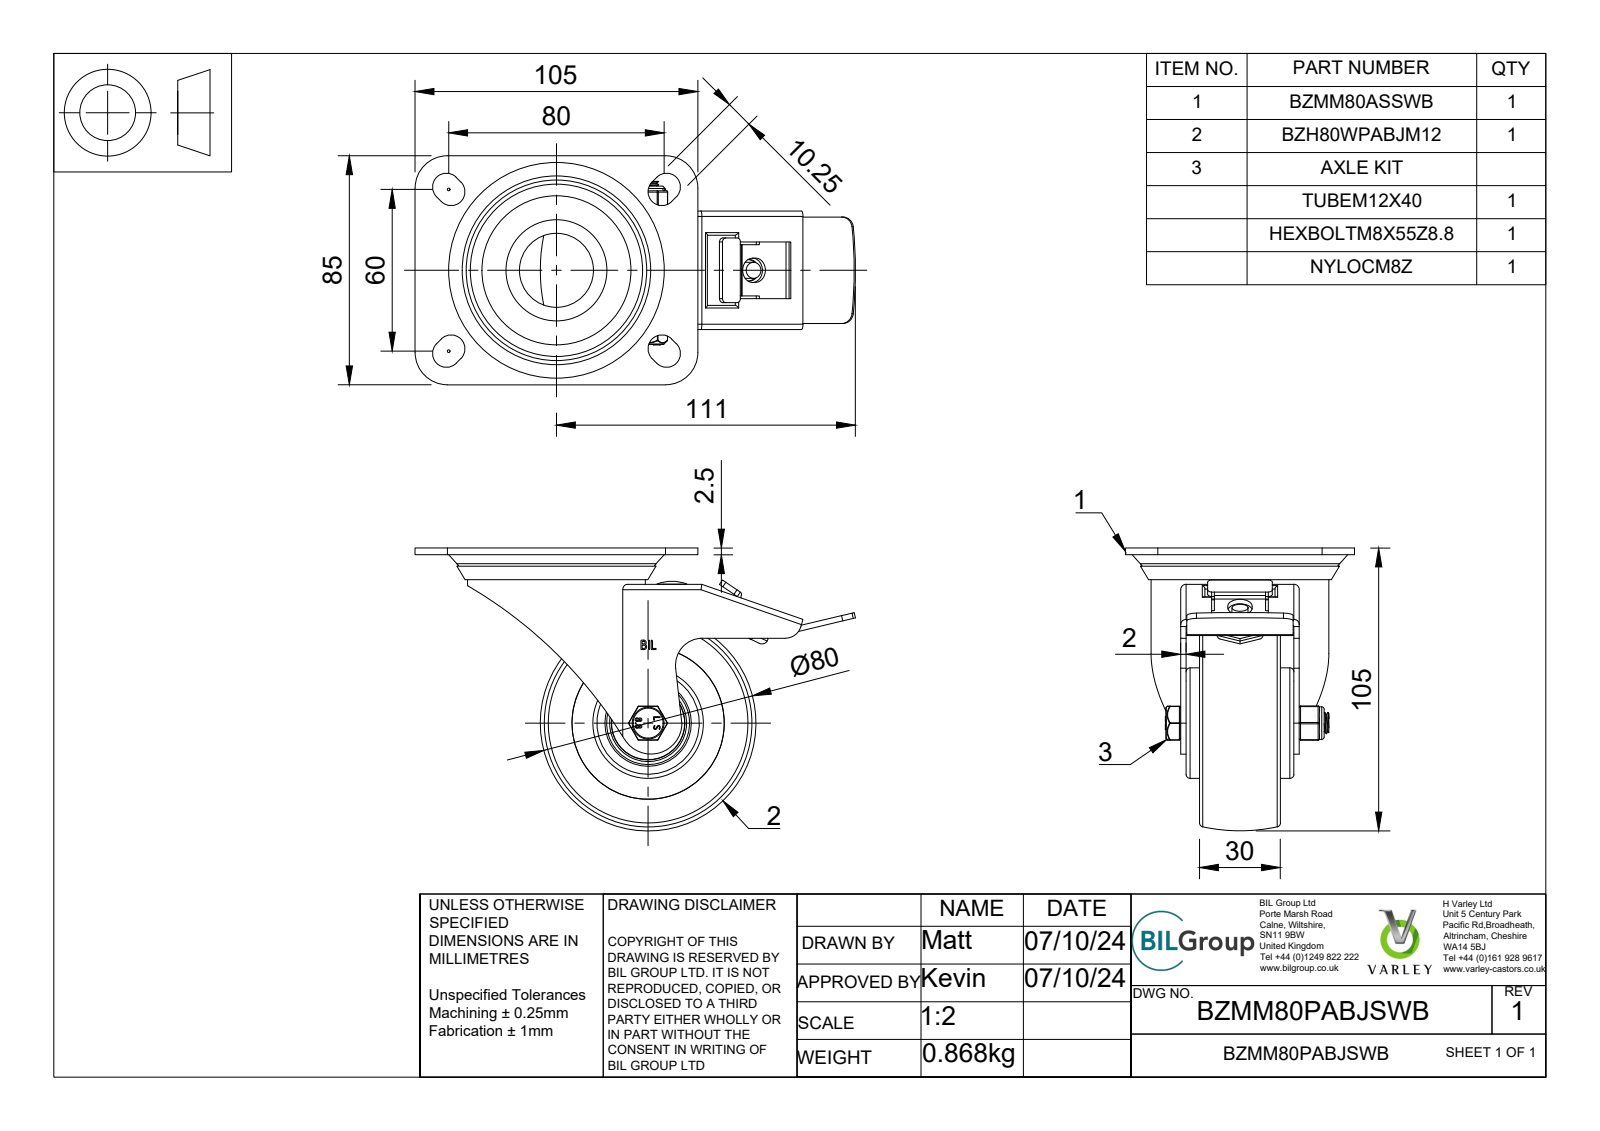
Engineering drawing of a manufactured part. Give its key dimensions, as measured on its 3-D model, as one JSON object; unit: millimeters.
{"part_name": "BZMM80PABJSWB v3; BZMM80ASSWB v1; ZINC PLATED, PRESSED STEEL TOP PLATE; ZINC PLATED, PRESSED STEEL TOP PLATE Geometry (+7 more)", "step_written_by": "Autodesk Translation Framework v13.20.0.188 (AUTOMOTIVE_DESIGN)", "units": "millimeters", "bodies": {"solids": 63, "faces": 1211, "planar": 503, "cylindrical": 230, "other": 478}, "overall_size": [163.5, 105, 85], "volume_mm3": 213053, "surface_area_mm2": 116581, "round_holes": [[0.66, 2], [8, 2], [6, 1], [8.2, 1], [8.4, 1], [8.6, 1], [12, 1], [18.45, 1], [18.64, 1], [20.6, 1], [26.14, 1], [27.34, 1]], "round_bosses_or_shafts": [[66, 1], [41, 1], [31.5, 1], [27.14, 1], [26.94, 1], [19.64, 1], [17, 1], [16, 1]], "partial_cylinders_radius": [[0.5, 24], [1, 14], [0.25, 12], [2, 11], [5.12, 8], [0.33, 4], [0.64, 4], [1.5, 4]], "face_to_face_distances": [2, 5, 2.5, 30, 35, 7, 0.5, 37, 42, 13], "hole_center_spacings": [3.22, 2.49, 42.86]}
